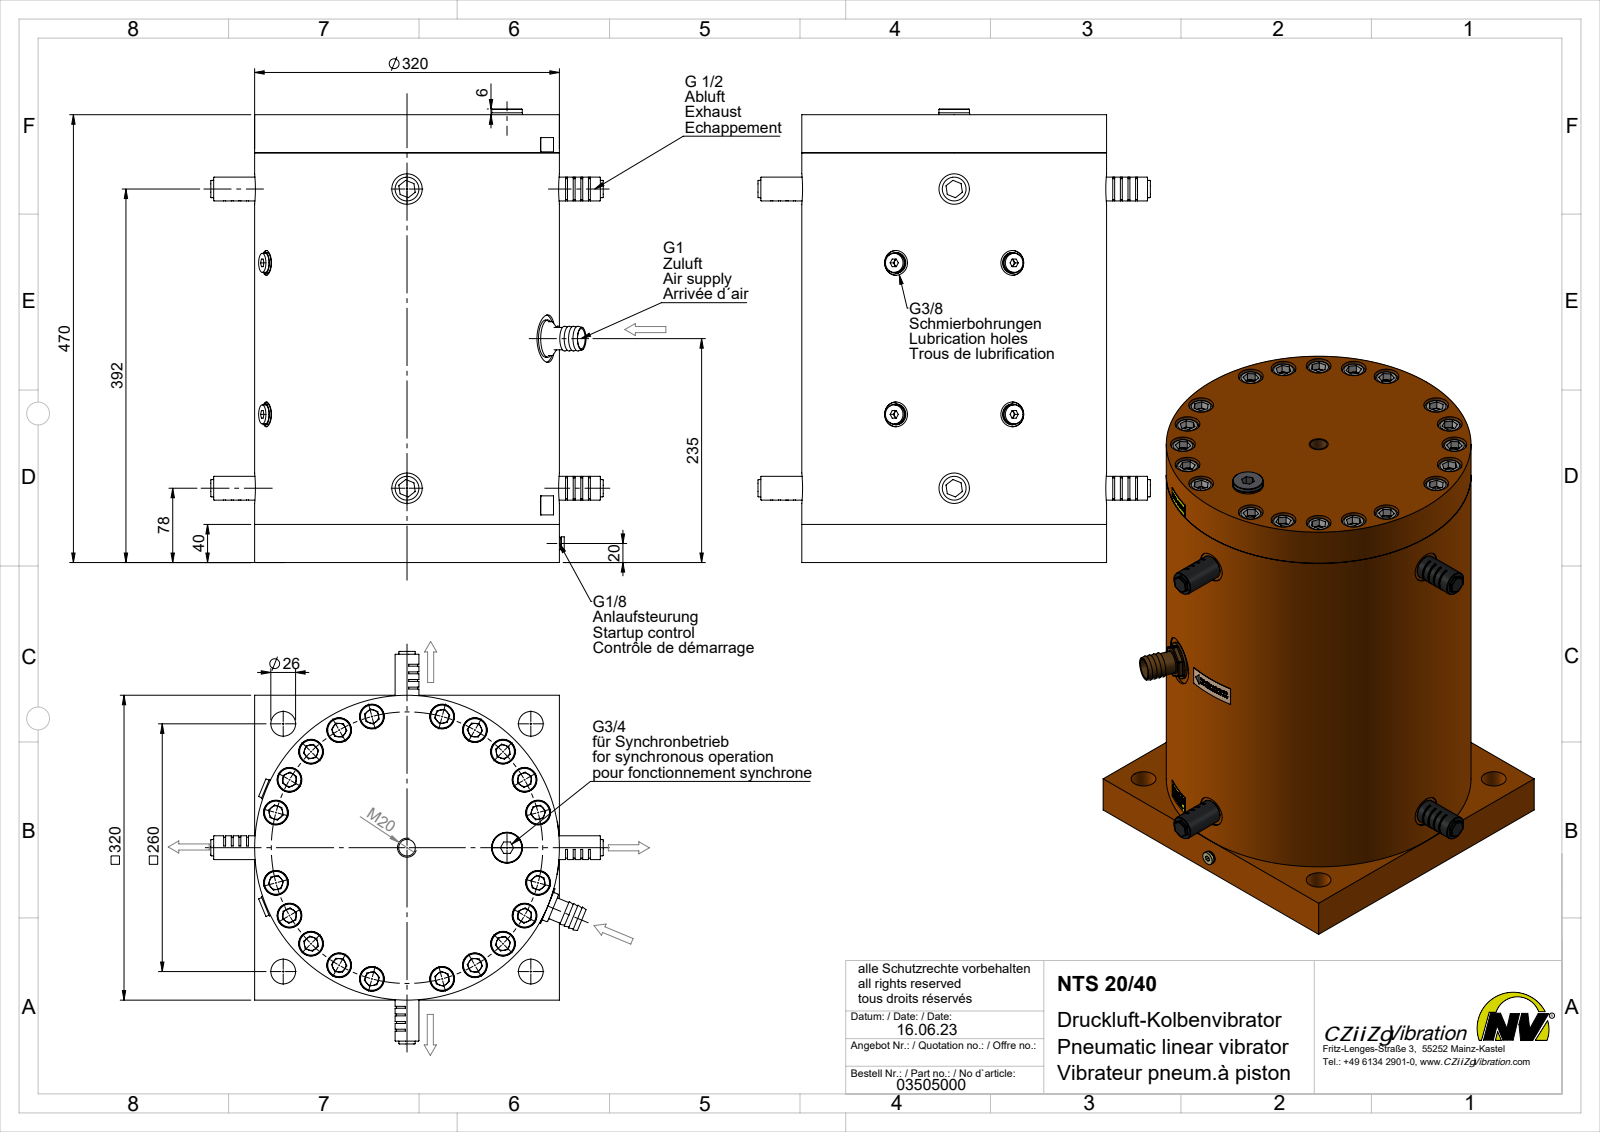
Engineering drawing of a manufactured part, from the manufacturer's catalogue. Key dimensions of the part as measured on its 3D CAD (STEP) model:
Part name (STEP PRODUCT): NTS 20-40 Kolbenvibrator #03505000
STEP written by: SolidWorks 2022 (AUTOMOTIVE_DESIGN)
Units: millimetres
Bodies: 107 solids, 7468 faces (5542 planar, 1246 cylindrical, 680 other)
Overall size (bounding box): 476 × 412 × 412
Volume: 19 330 000 mm³ · Surface area: 1 722 000 mm²
Round holes (diameter × count): ⌀26 ×28, ⌀14 ×20, ⌀17 ×20, ⌀2 ×6, ⌀9.6 ×4, ⌀14.95 ×4, ⌀17.1 ×4, ⌀18.63 ×4, ⌀32 ×4, ⌀6 ×1, ⌀8.57 ×1, ⌀10 ×1
Round bosses / shafts (diameter × count): ⌀25.4 ×20, ⌀24 ×20, ⌀16 ×20, ⌀25 ×4, ⌀22 ×4, ⌀21.8 ×4, ⌀20.96 ×4, ⌀20 ×4
Partial cylindrical surfaces — rounded edges, fillets, slot ends (radius × count): R0.5 ×156, R1 ×18, R160.2 ×1
Main face-to-face distances: 40, 430, 390, 39, 429, 469, 1, 470, 320, 409
Hole centre spacings: 142.5, 37.2, 109.06, 226.1, 263.3, 282.56, 73.76, 201.52
